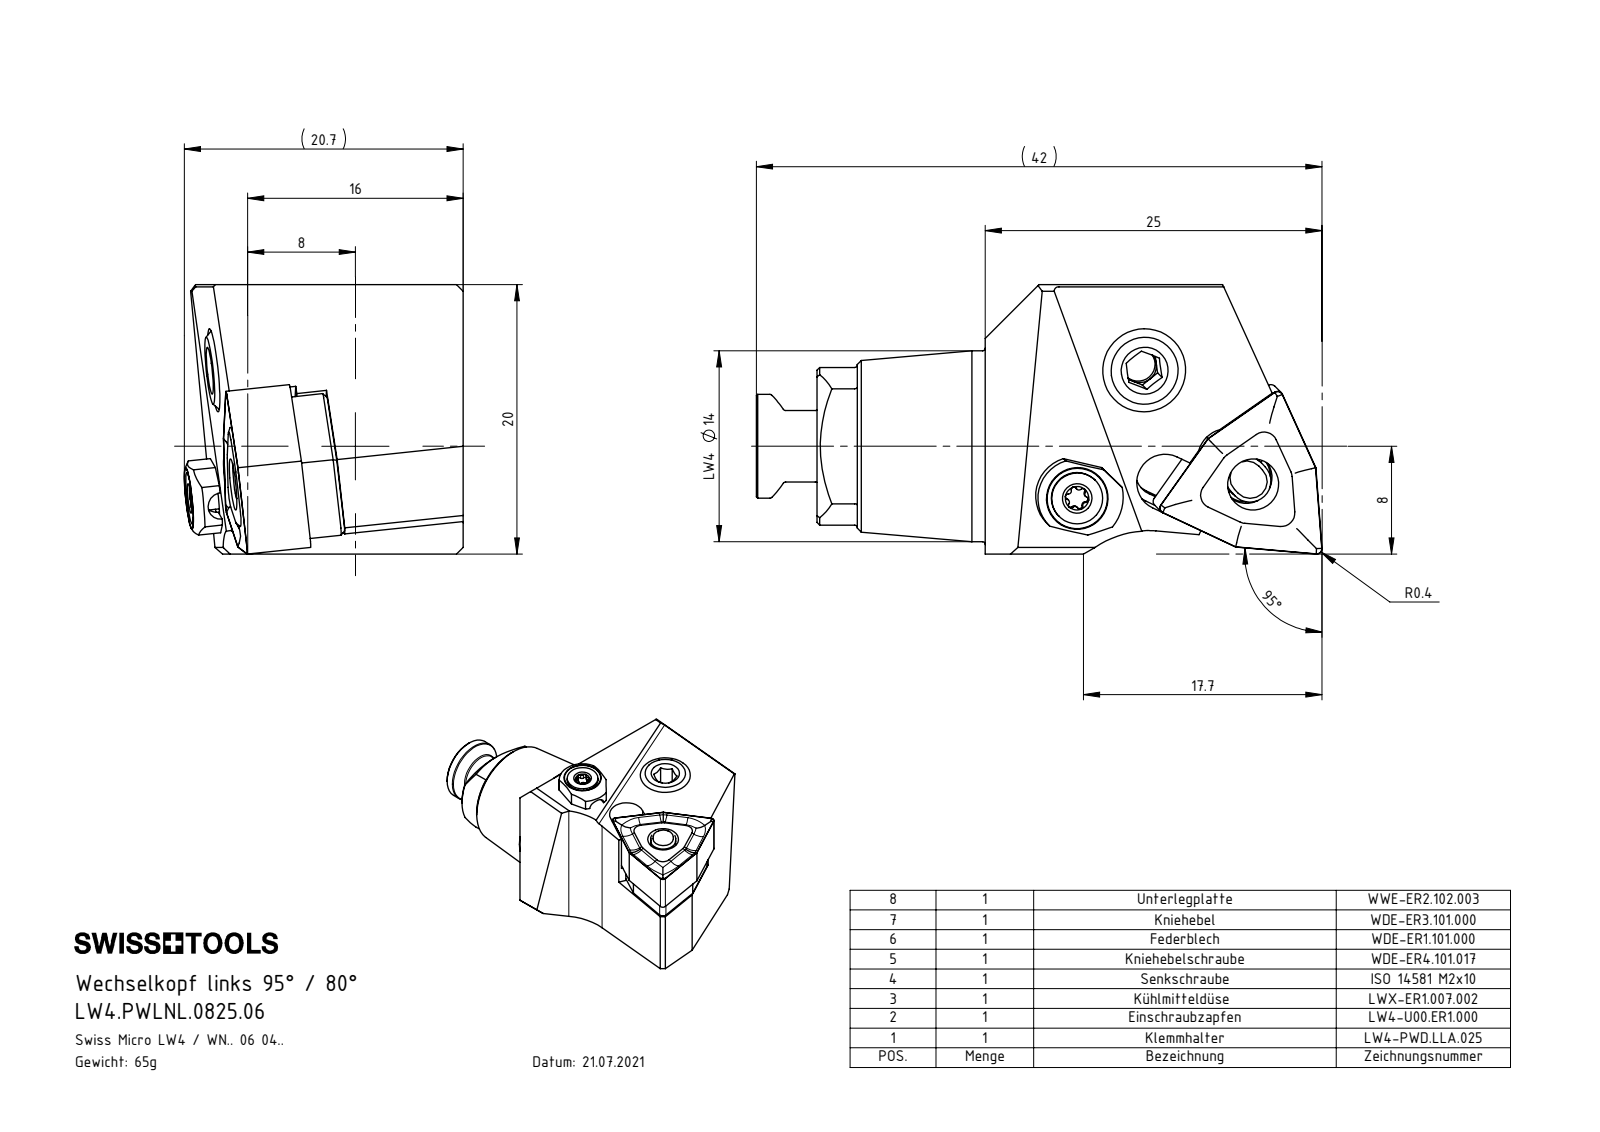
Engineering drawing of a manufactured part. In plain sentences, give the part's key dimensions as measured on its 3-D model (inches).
The part is named "LW4-PWD.LLA.025_A; WDE-ER4.101.017_A; WNMG060404; WDE-ER1.101.000 (+5 more)". Its 3-D file was written by "SolidWorks 2022 (CONFIG_CONTROL_DESIGN)". It is 8 solids with 401 faces: 151 planar, 92 cylindrical and 158 other. Overall it measures 1.654 by 0.815 by 0.787 inches. Its volume is 0.481 cubic inches and its surface area 8.187 square inches. Round holes: 3 of diameter 0.118, 2 of diameter 0.098, 1 of diameter 0.063, 1 of diameter 0.079, 1 of diameter 0.15, 1 of diameter 0.197, 1 of diameter 0.217, 1 of diameter 0.252. Round bosses or shafts: 2 of diameter 0.236, 1 of diameter 0.558, 1 of diameter 0.303, 1 of diameter 0.232, 1 of diameter 0.209, 1 of diameter 0.197, 1 of diameter 0.15, 1 of diameter 0.122. Partial cylindrical surfaces (rounded edges, fillets, slot ends): 8 of radius 0.008, 6 of radius 0.009, 5 of radius 0.083, 3 of radius 0.016, 2 of radius 0.039, 1 of radius 0.02, 1 of radius 0.071, 1 of radius 0.087. The main face-to-face distances are 0.787, 0.165, 0.026, 0.283, 0.295, 0.295, 0.079, 0.073, 0.118, 0.185. The hole center spacings are 0.419, 0.419, 0.465, 0.526.
